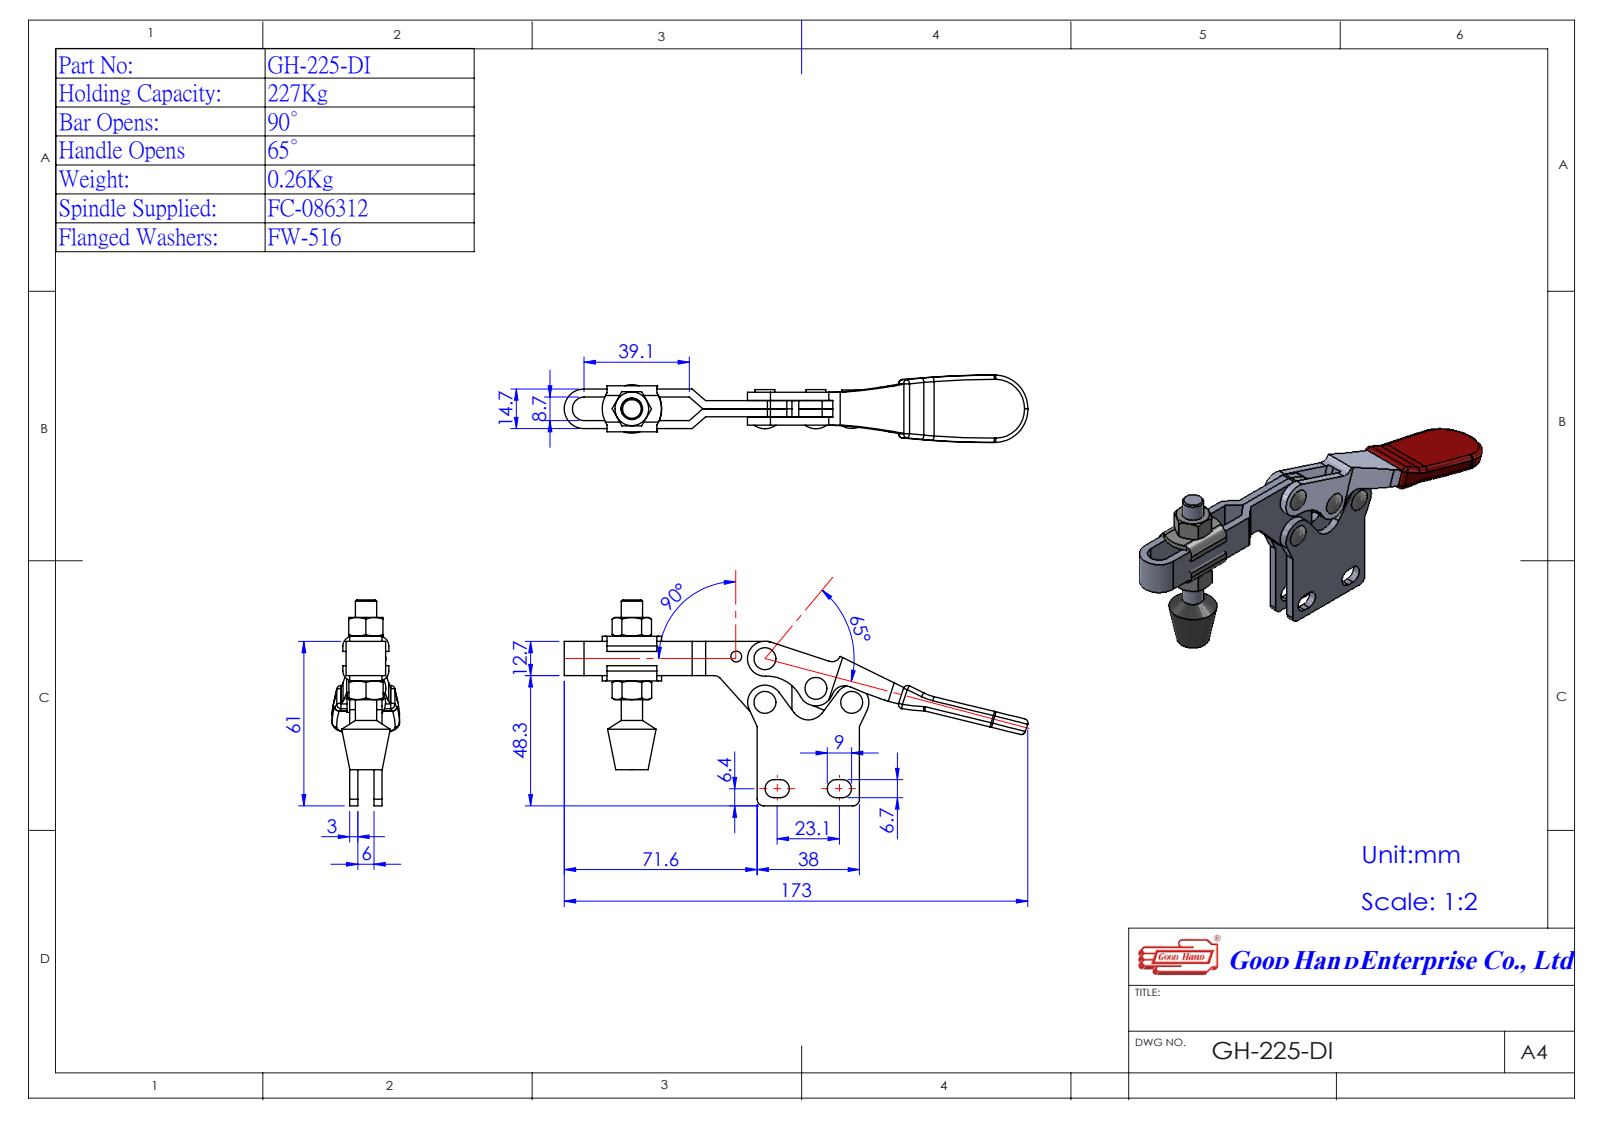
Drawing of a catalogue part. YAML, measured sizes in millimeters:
part_name: "Group2^GH-225-DI(簡化); GH-225-DI(簡化)-1; Group1^GH-225-DI(簡化)-1; Group5^GH-225-DI(簡化)-1 (+2 more)"
step_written_by: "SolidWorks 2016 (AUTOMOTIVE_DESIGN)"
units: millimeters
bodies: {solids: 4, faces: 275, planar: 120, cylindrical: 128, other: 27}
overall_size: [173.56, 76.44, 25]
volume: 27229
surface_area: 27320
round_holes:
  - {diameter: 5, count: 4}
round_bosses_or_shafts:
  - {diameter: 7.35, count: 4}
  - {diameter: 6.35, count: 2}
  - {diameter: 6.3, count: 2}
  - {diameter: 7.93, count: 1}
  - {diameter: 4, count: 1}
partial_cylinders:
  - {radius: 3, count: 5}
  - {radius: 1.2, count: 4}
  - {radius: 3.35, count: 4}
  - {radius: 3.6, count: 4}
  - {radius: 11.04, count: 4}
  - {radius: 6.4, count: 3}
  - {radius: 6.5, count: 3}
  - {radius: 2.5, count: 2}
face_to_face_distances: [3, 6, 9, 3.1, 6.1, 9.1, 12, 6.01, 3.01, 2.99]
hole_center_spacings: [14.25, 16.2, 19.63, 21.9, 32.2, 36.05]
